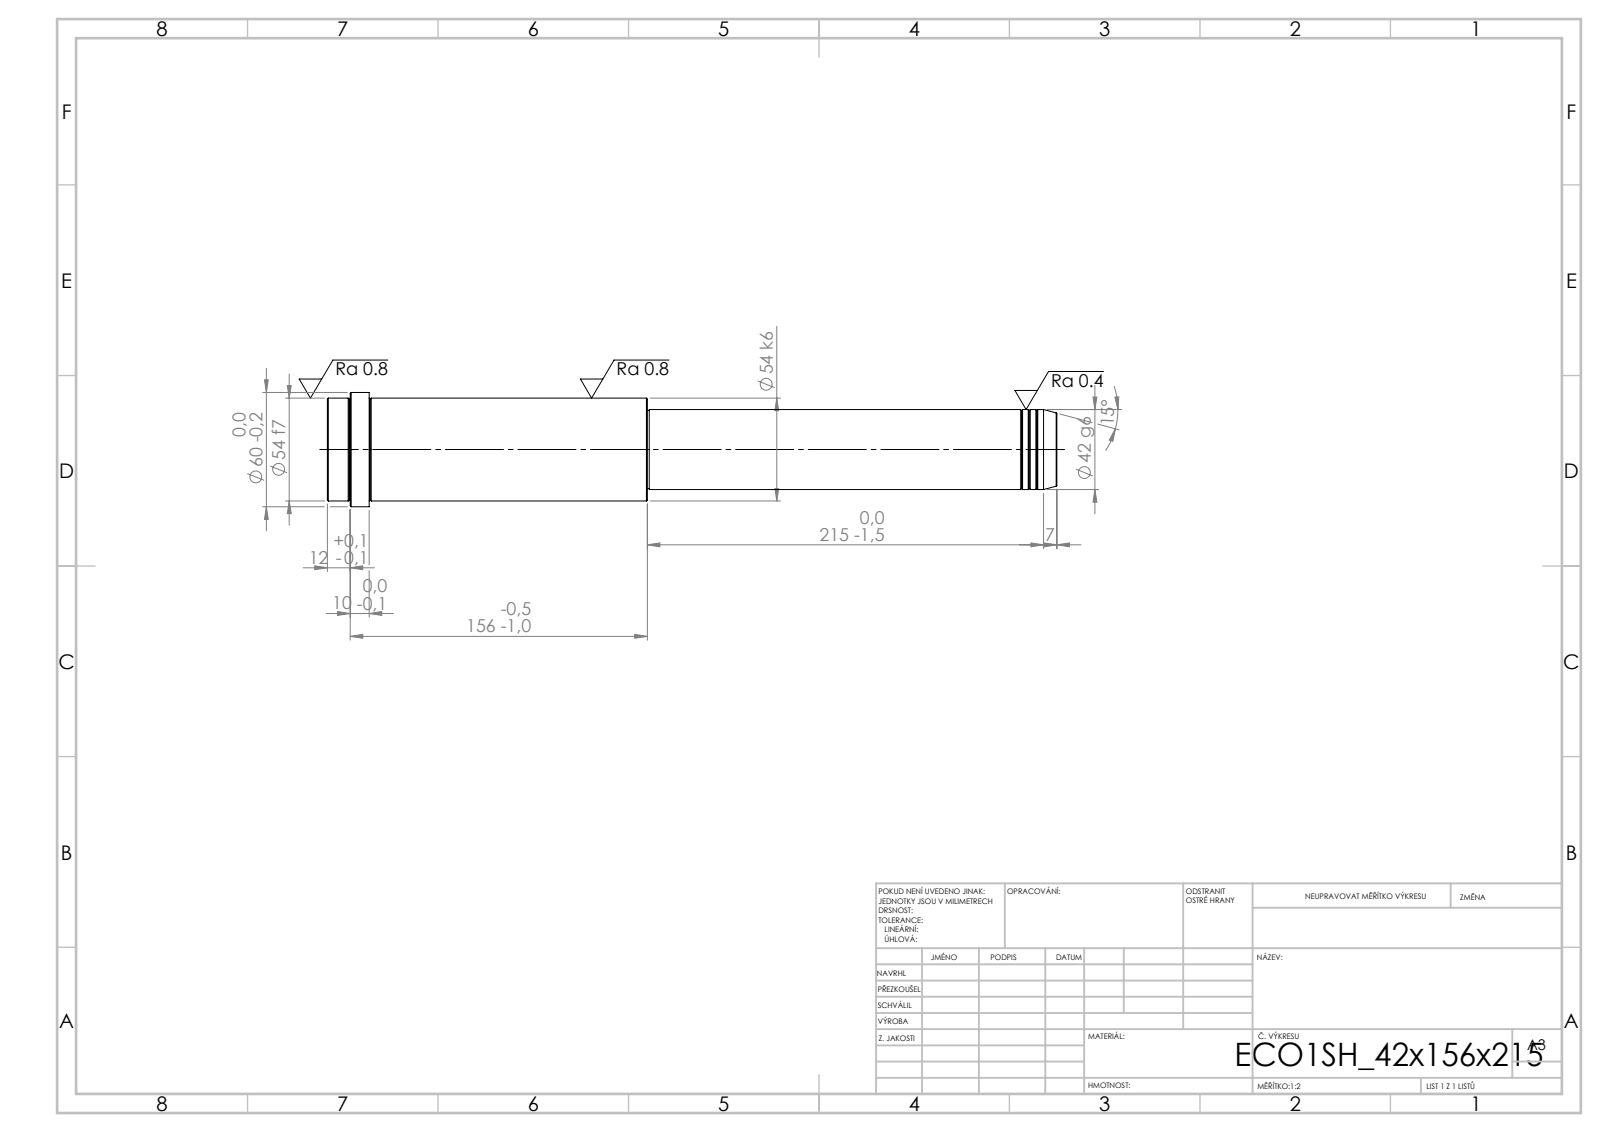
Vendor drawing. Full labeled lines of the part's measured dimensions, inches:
STEP written by: SolidWorks 2019 (CONFIG_CONTROL_DESIGN)
Units: inches
Bodies: 1 solid, 52 faces (6 planar, 16 cylindrical, 30 other)
Overall size (bounding box): 15.079 × 2.362 × 2.362
Volume: 41.91 in³ · Surface area: 97.38 in²
Round bosses / shafts (diameter × count): ⌀2.362 ×1, ⌀2.126 ×1, ⌀1.654 ×1, ⌀1.614 ×1
Main face-to-face distances: 15.079, 8.465, 6.614, 14.213, 5.748, 0.866, 14.606, 6.142, 0.394, 0.472
